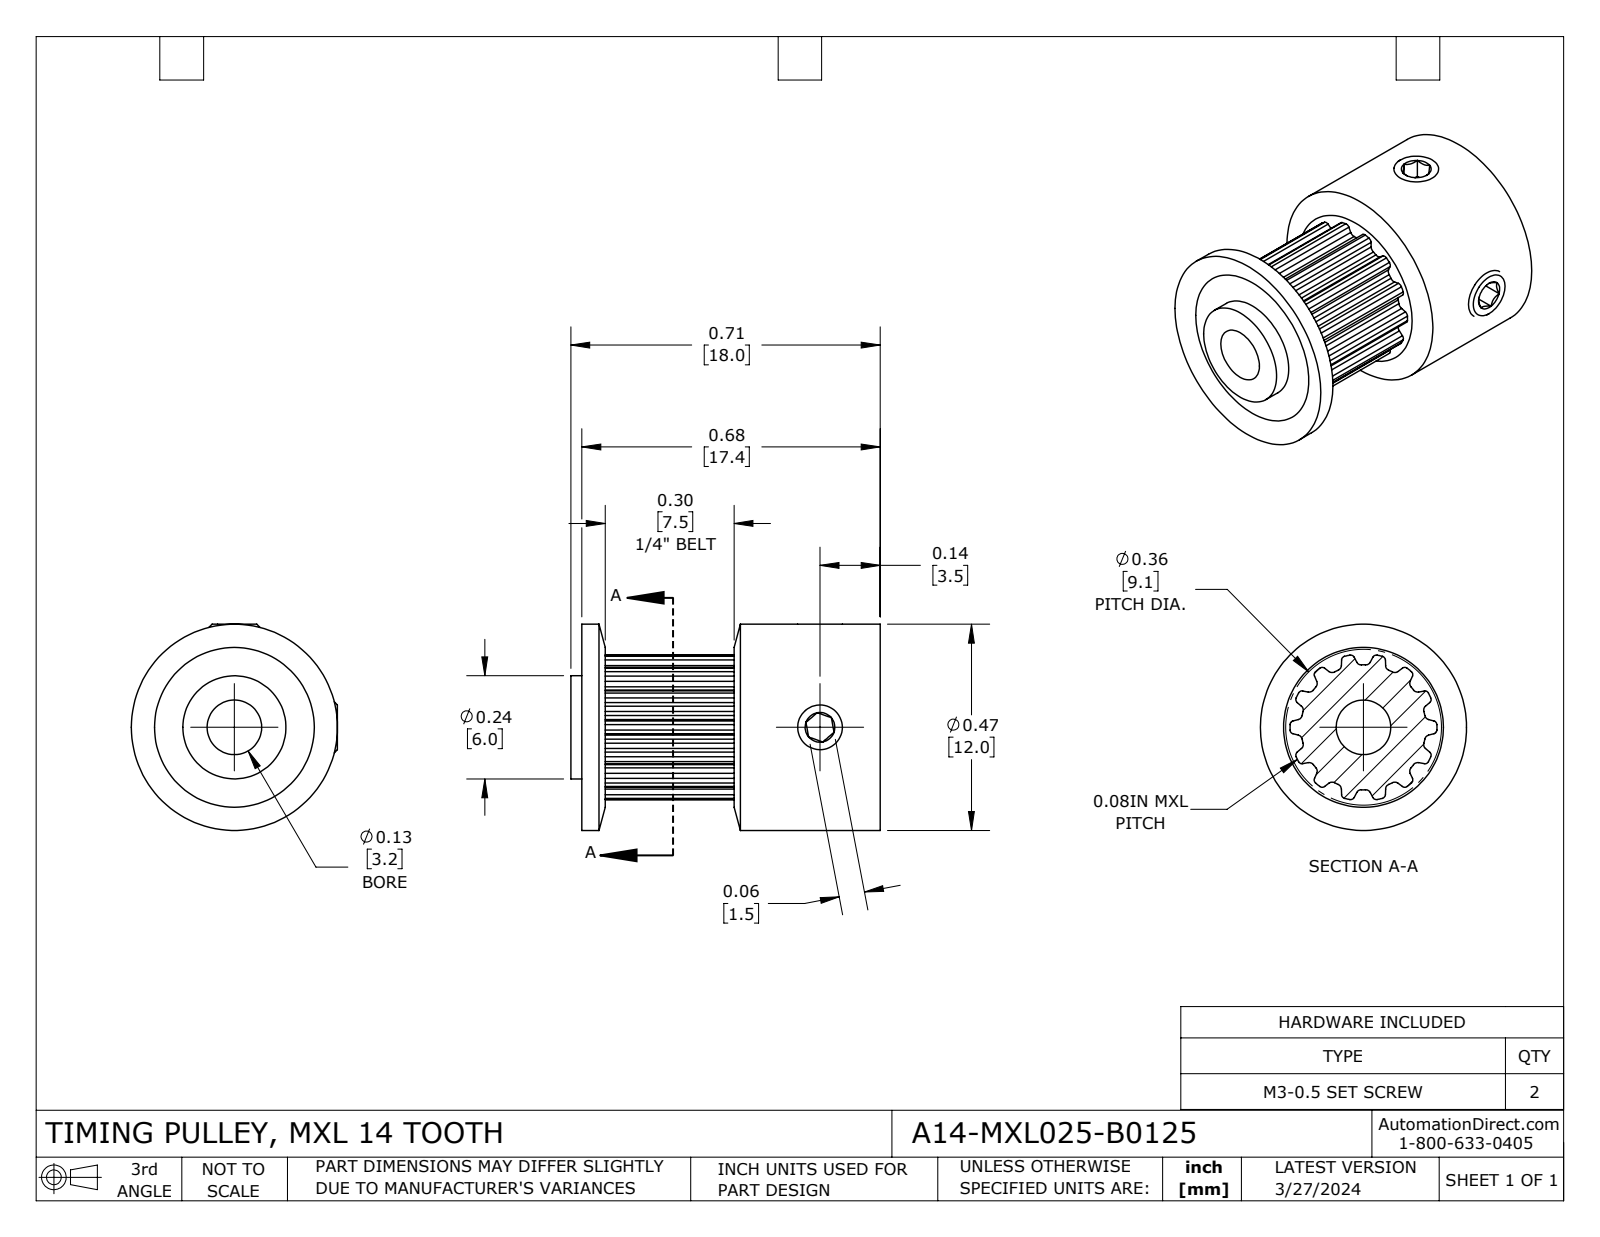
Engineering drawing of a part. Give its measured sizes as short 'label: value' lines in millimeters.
name: A14-MXL025-B0125
written by: SolidWorks 2021 (CONFIG_CONTROL_DESIGN)
unit: mm
bodies: 3 solids, 190 faces (49 planar, 109 cylindrical, 32 other)
size: 18 × 12 × 12
volume: 1 310 mm³; area: 1 286 mm²
holes: 2× ⌀2.5, 1× ⌀3.17
bosses: 2× ⌀3, 1× ⌀12, 1× ⌀6
rounds: 28× R0.23, 28× R0.3, 1× R3.63, 1× R4.28
face distances: 17, 1, 8.5, 2.86, 18, 2, 16, 9.5, 7.5, 3
